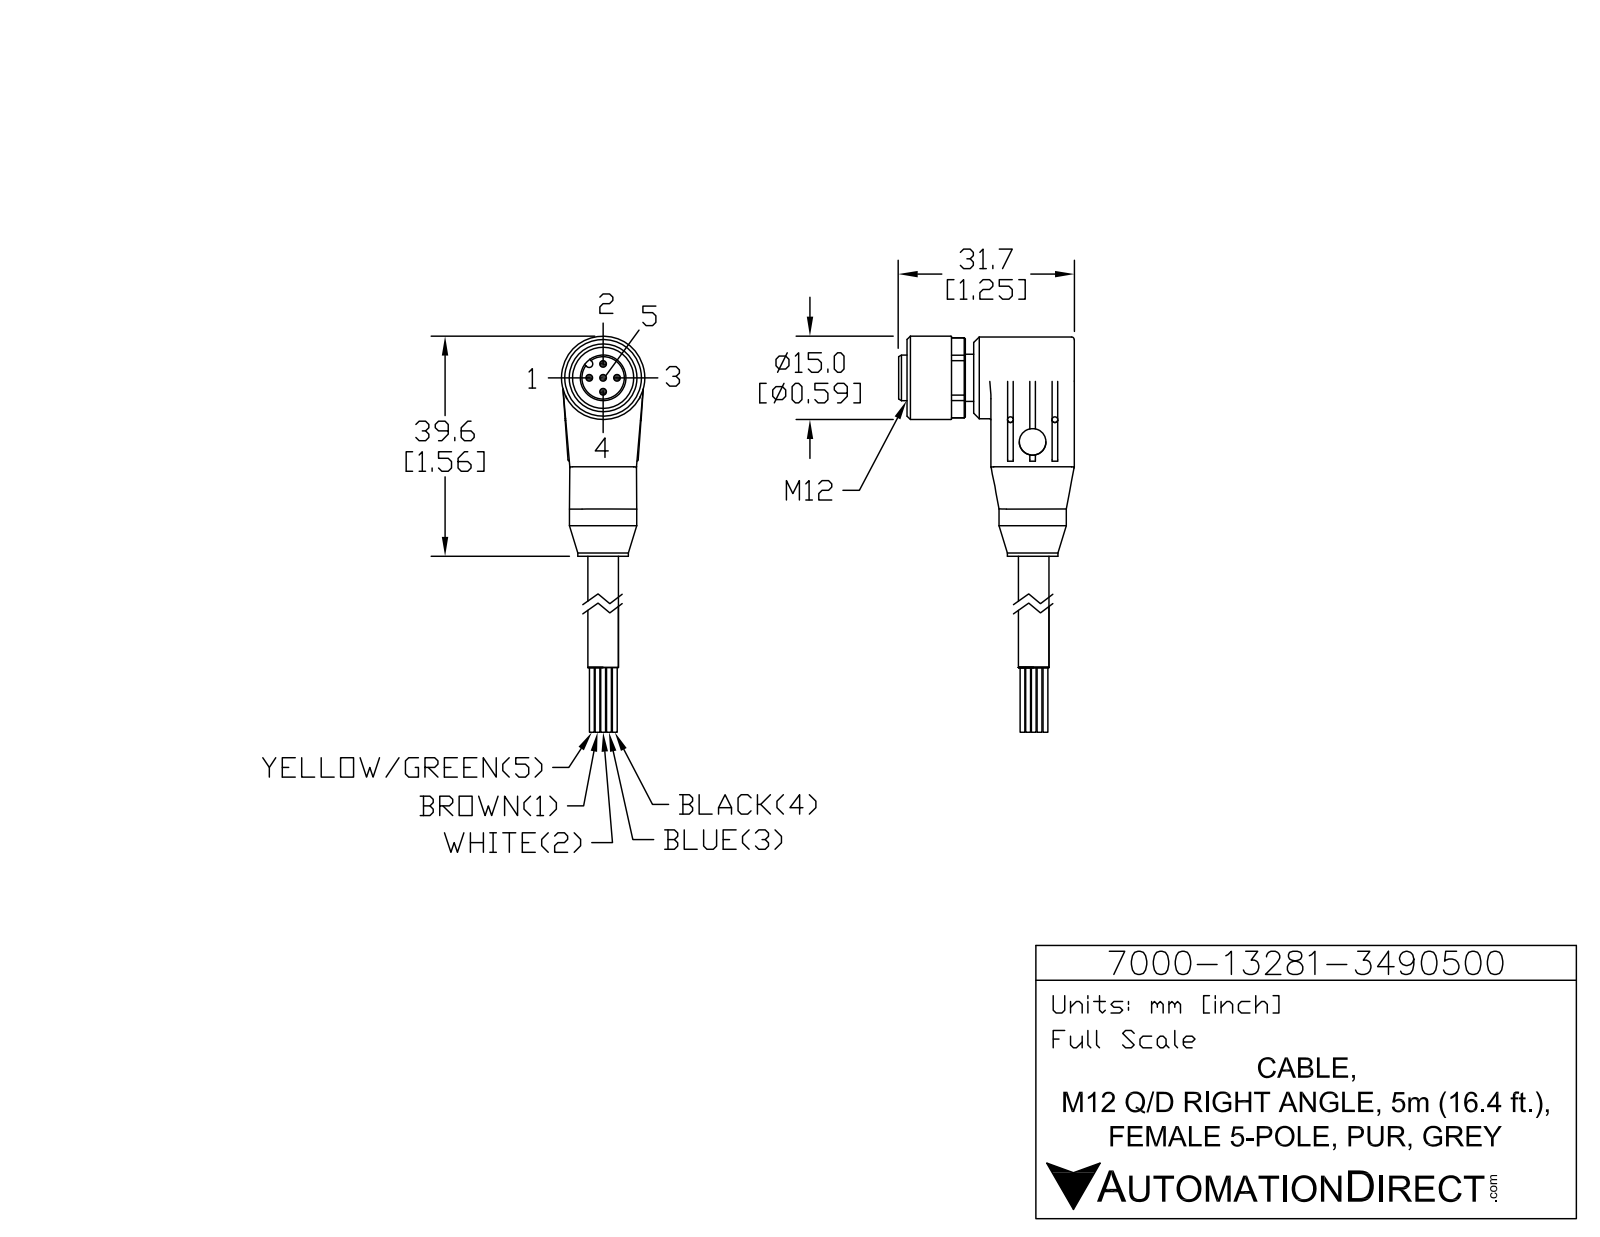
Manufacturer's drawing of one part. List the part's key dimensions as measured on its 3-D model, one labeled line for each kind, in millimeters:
Part name (STEP PRODUCT): 7000-13281-3490500
STEP written by: SolidWorks 2015 (AUTOMOTIVE_DESIGN)
Units: millimetres
Bodies: 1 solid, 165 faces (70 planar, 61 cylindrical, 34 other)
Overall size (bounding box): 59.6 × 31.6 × 15
Volume: 9 143 mm³ · Surface area: 4 032 mm²
Round holes (diameter × count): ⌀1.2 ×5, ⌀1.05 ×4, ⌀4.8 ×1, ⌀11 ×1
Round bosses / shafts (diameter × count): ⌀15 ×1, ⌀14.7 ×1, ⌀12.1 ×1, ⌀9.1 ×1, ⌀8.5 ×1, ⌀8.2 ×1, ⌀6.5 ×1
Partial cylindrical surfaces — rounded edges, fillets, slot ends (radius × count): R0.5 ×4, R0.3 ×2, R0.65 ×1, R7.2 ×1
Main face-to-face distances: 15, 1.5, 19.6, 4.6, 12, 18.1, 3.1, 3, 7.6, 16.6
Hole centre spacings: 2.5, 3.54, 5, 8
